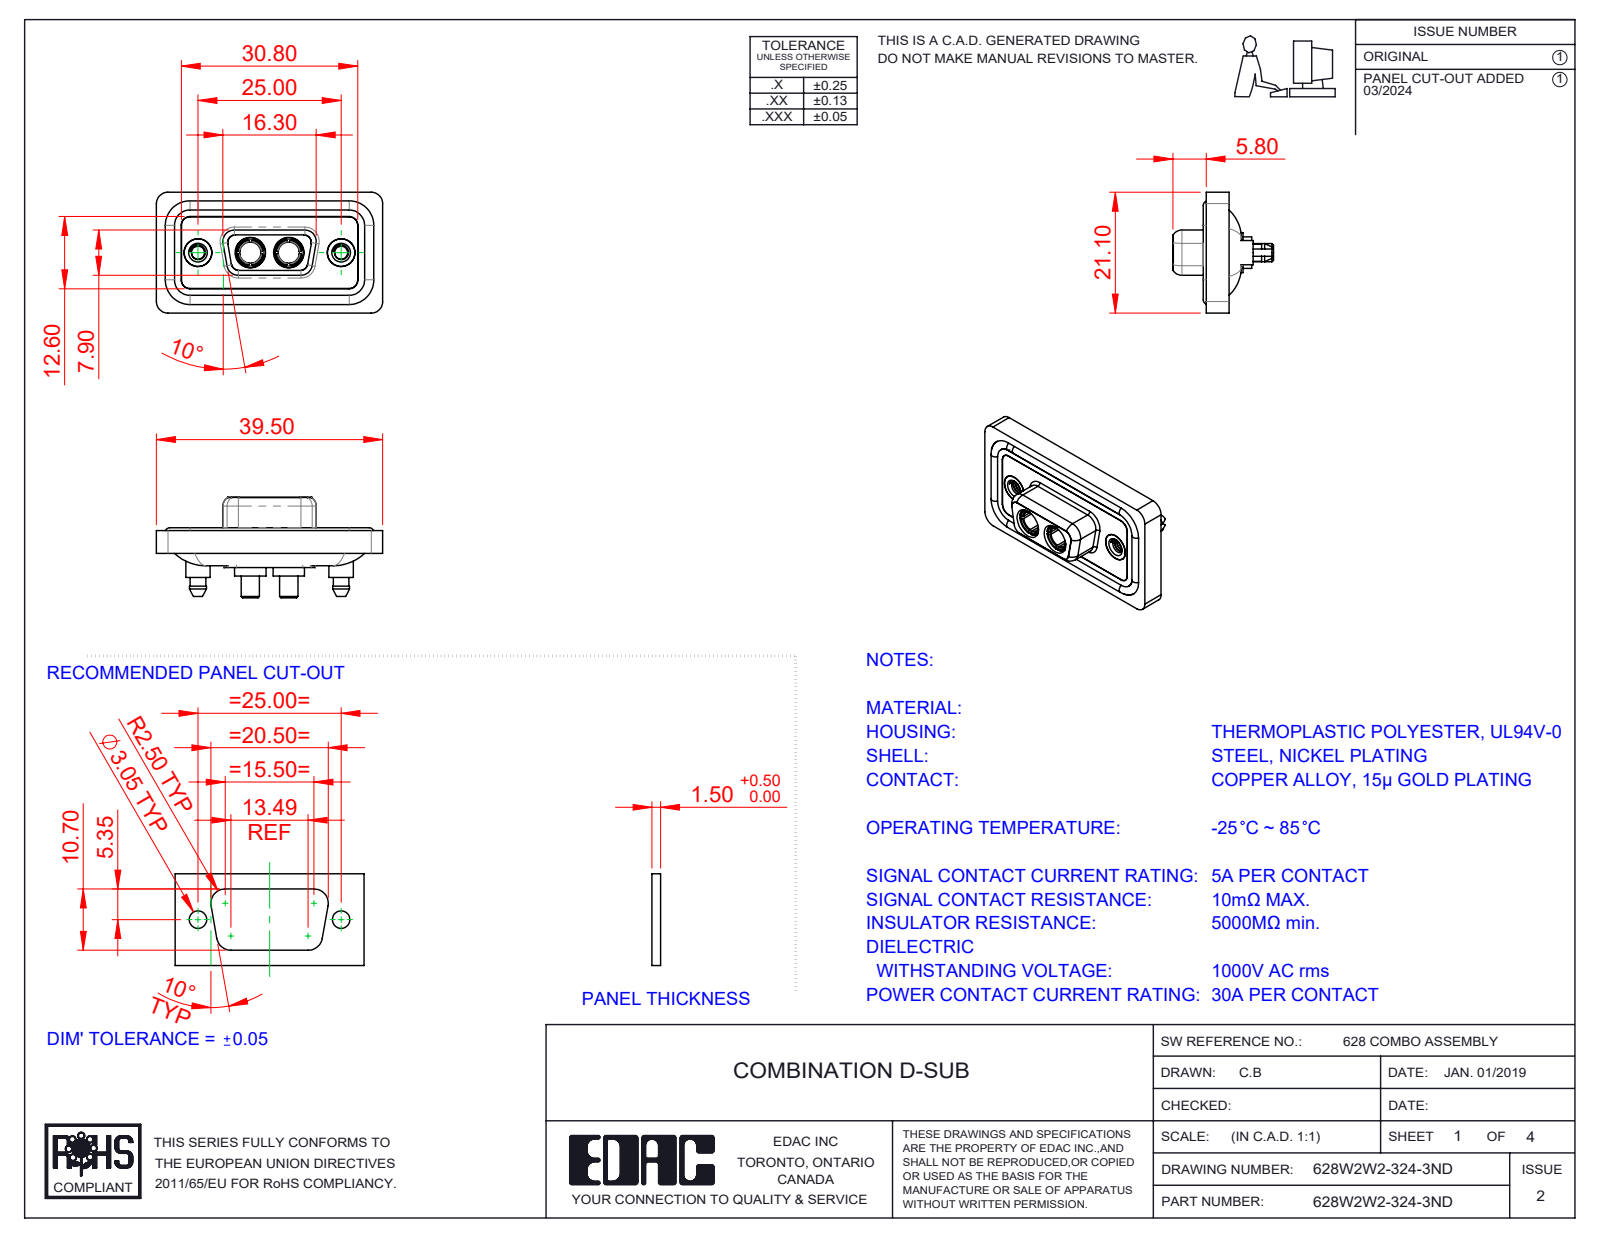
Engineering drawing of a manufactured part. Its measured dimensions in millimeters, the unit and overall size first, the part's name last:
Units: millimetres
Overall size (bounding box): 39.5 × 21.1 × 17.55
Round holes (diameter × count): ⌀4.85 ×4, ⌀2.26 ×2, ⌀3.7 ×2, ⌀4 ×2, ⌀4.05 ×2, ⌀5 ×2, ⌀5.3 ×2
Round bosses / shafts (diameter × count): ⌀1.6 ×4, ⌀5.5 ×2, ⌀5.4 ×2, ⌀5.2 ×2, ⌀4.96 ×2, ⌀4.95 ×2, ⌀4.8 ×2, ⌀4.75 ×2
Partial cylindrical surfaces — rounded edges, fillets, slot ends (radius × count): R1.5 ×24, R2 ×18, R1.6 ×10, R1.35 ×8, R0.25 ×4, R0.5 ×4, R0.6 ×4, R0.65 ×4
Main face-to-face distances: 0.4, 1.8, 1.1, 2.9, 1.6, 0.5, 5.65, 7.45, 1.5, 4
Hole centre spacings: 9.14, 15.86, 6.72, 25
Volume: 4 862 mm³ · Surface area: 7 984 mm²
Bodies: 11 solids, 600 faces (179 planar, 282 cylindrical, 139 other)
Part name (STEP PRODUCT): 628Combo Shell Front_09 Contacts; Power Socket_30A S; 628Combo Waterproof Housing_09 Contacts; 628W2W2-324-3ND (+3 more)
STEP written by: SolidWorks 2023 (CONFIG_CONTROL_DESIGN)
